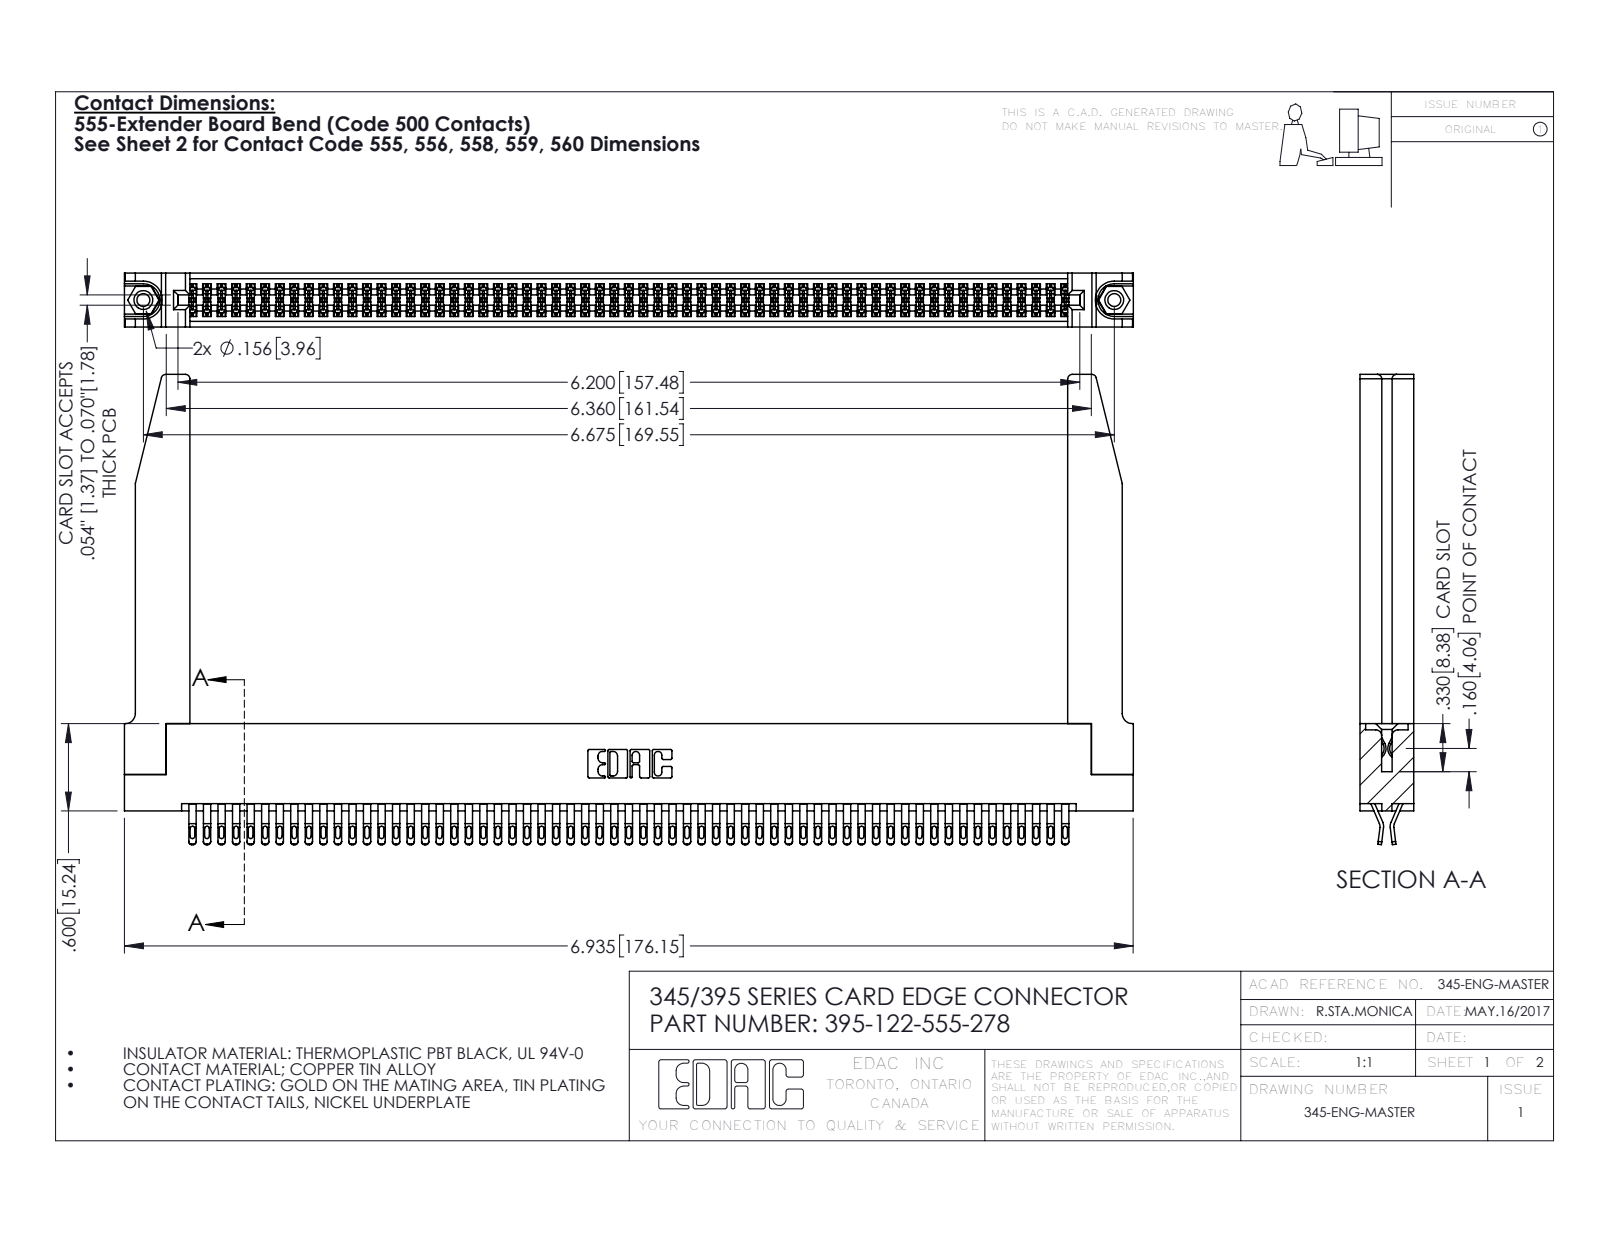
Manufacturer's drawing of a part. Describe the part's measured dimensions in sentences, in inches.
The part is named "395-122-555-278; 345-250-001_345-250-001-102; 345 Part_Flush Mounting Lugs - 0.156 Dia-TH; 345-292-001_555 Tail (+1 more)". Its 3-D file was written by "SolidWorks 2016 (CONFIG_CONTROL_DESIGN)". It is 127 solids with 7192 faces: 4004 planar, 3136 cylindrical and 52 other. Overall it measures 6.936 by 3.232 by 0.37 inches. Its volume is 1.551 cubic inches and its surface area 53.5 square inches. Round holes: 2 of diameter 0.089, 2 of diameter 0.125, 2 of diameter 0.156, 1 of diameter 0.064. Round bosses or shafts: 2 of diameter 0.155. Partial cylindrical surfaces (rounded edges, fillets, slot ends): 305 of radius 0.016, 244 of radius 0.02, 183 of radius 0.006, 22 of radius 0.01, 8 of radius 0.03, 6 of radius 0.007, 6 of radius 0.031, 3 of radius 0.026. The main face-to-face distances are 0.072, 0.298, 0.37, 0.025, 0.2, 0.098, 0.272, 0.225, 0.175, 0.148. The hole center spacings are 0.27, 6.439, 6.675.
